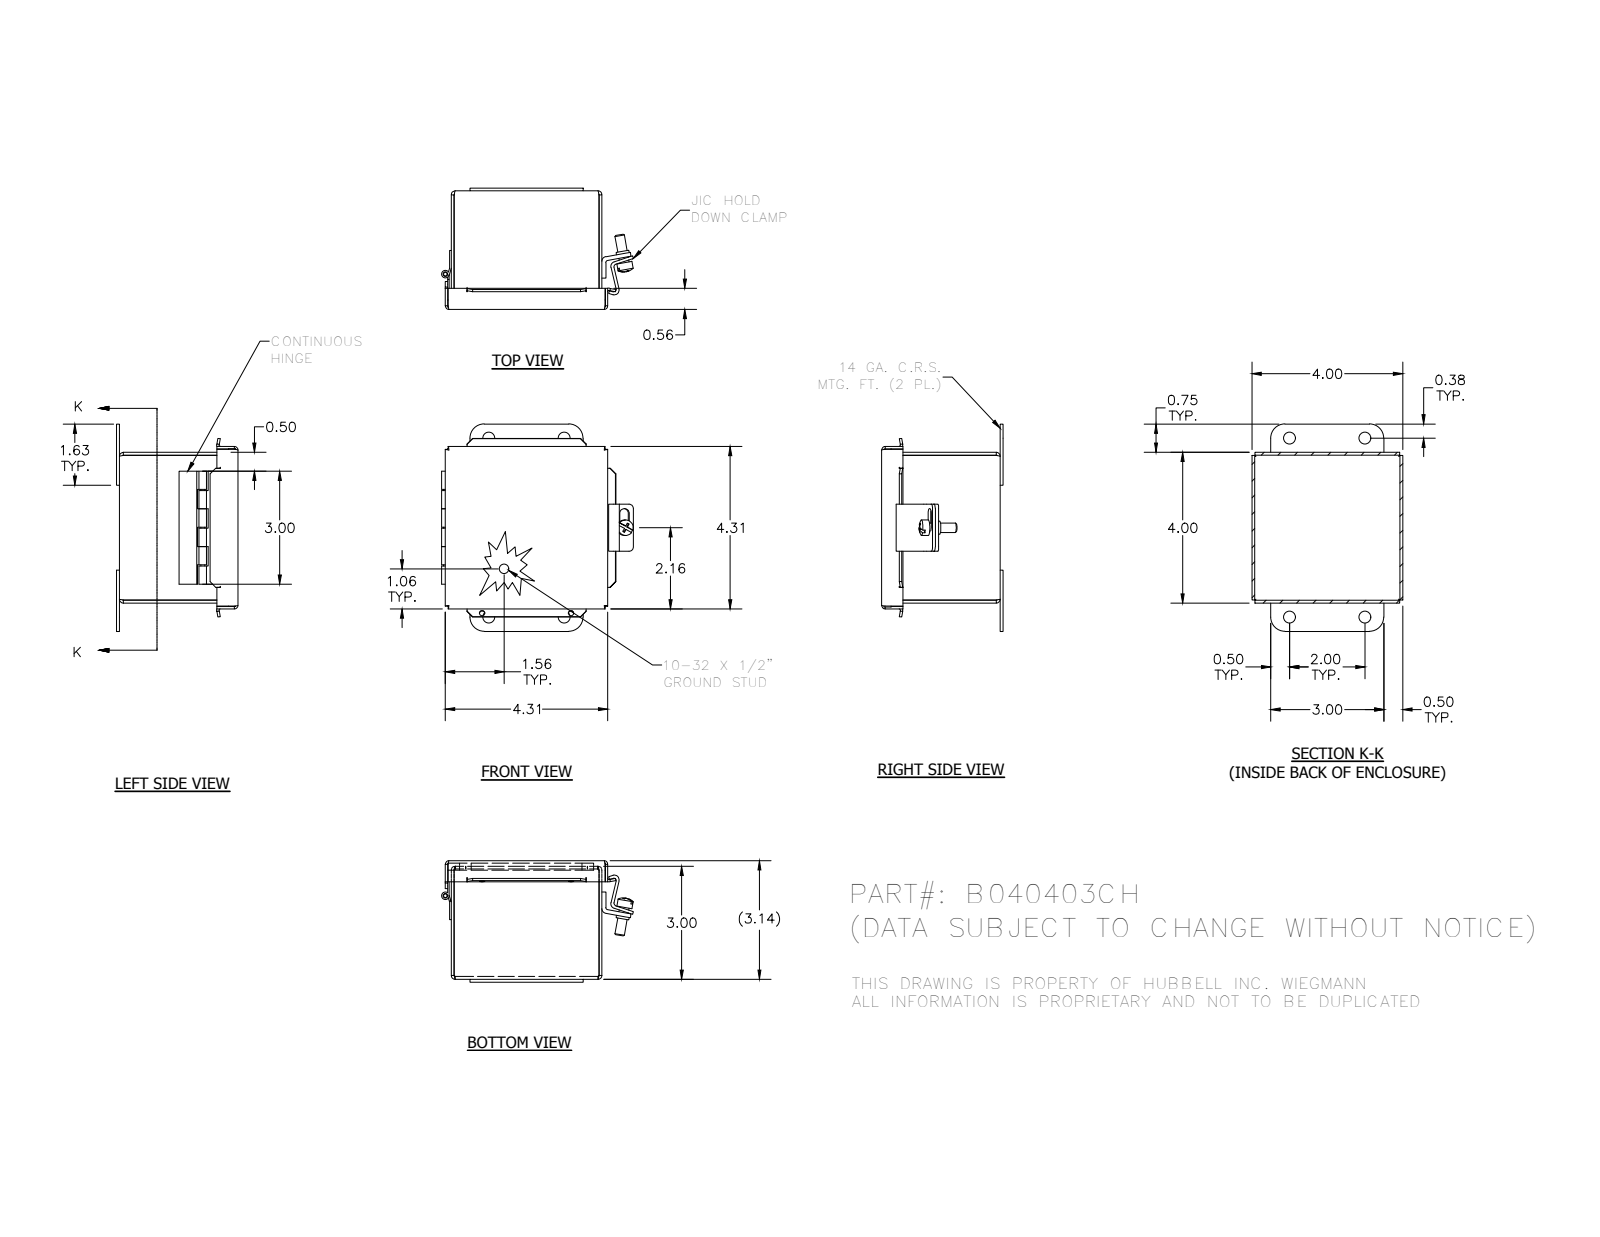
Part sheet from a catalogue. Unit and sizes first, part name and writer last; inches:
Units: inches
Overall size (bounding box): 5.5 × 5.087 × 3.219
Round holes (diameter × count): ⌀0.31 ×4, ⌀0.14 ×2, ⌀0.116 ×1, ⌀0.196 ×1
Round bosses / shafts (diameter × count): ⌀0.25 ×2, ⌀0.41 ×1, ⌀0.344 ×1, ⌀0.2 ×1, ⌀0.19 ×1, ⌀0.1 ×1
Partial cylindrical surfaces — rounded edges, fillets, slot ends (radius × count): R0.031 ×15, R0.105 ×8, R0.093 ×7, R0.125 ×4, R0.375 ×4, R0.063 ×3, R0.126 ×3, R0.133 ×2
Main face-to-face distances: 0.074, 3.926, 3.083, 4, 3.852, 3.144, 0.062, 3.009, 3.07, 0.093
Hole centre spacings: 2, 4.75, 5.154, 2.357
Volume: 9.521 in³ · Surface area: 256.1 in²
Bodies: 13 solids, 330 faces (229 planar, 71 cylindrical, 30 other)
Part name (STEP PRODUCT): B040403CH; 3481; C1001; C1002 (+8 more)
STEP written by: Autodesk Inventor 2012 (AUTOMOTIVE_DESIGN)
